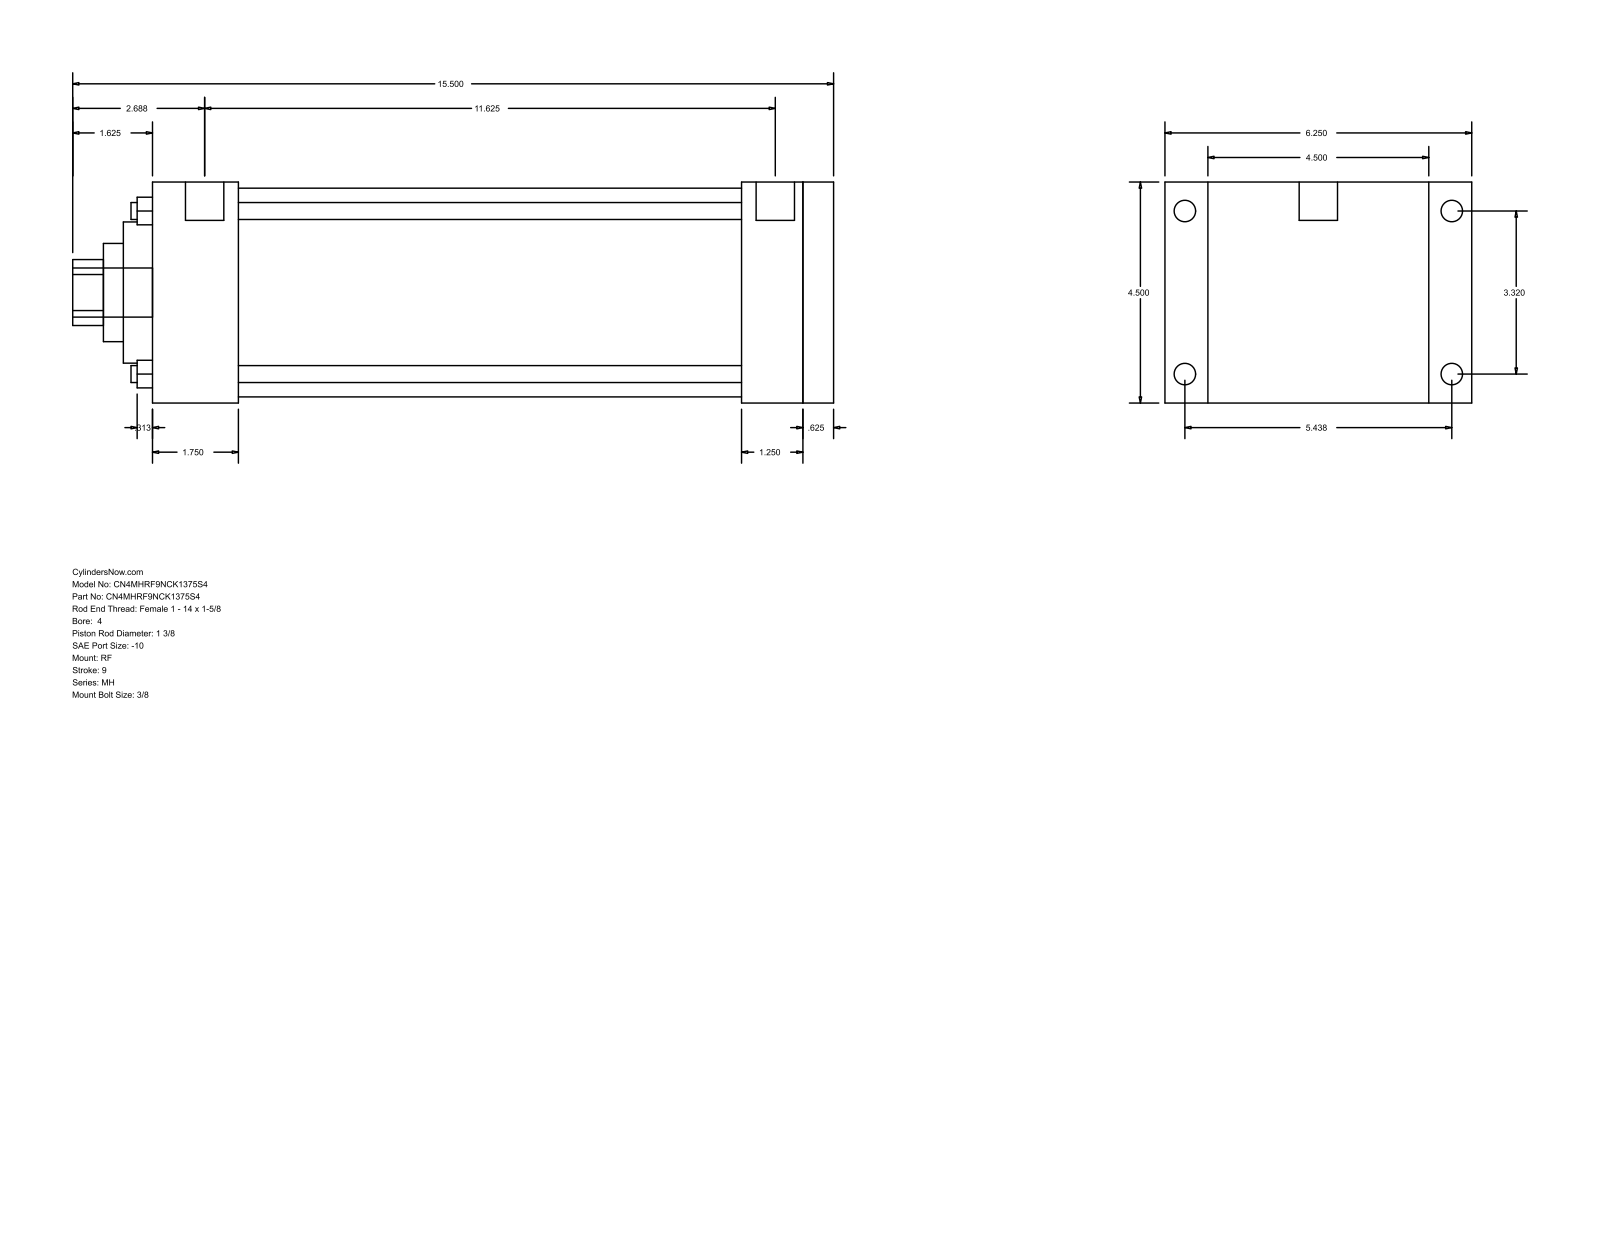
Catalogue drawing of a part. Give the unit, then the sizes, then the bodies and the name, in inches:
Units: inches
Overall size (bounding box): 15.5 × 6.25 × 4.5
Round holes (diameter × count): ⌀0.345 ×4, ⌀1.375 ×1, ⌀2 ×1, ⌀2.875 ×1, ⌀4.25 ×1
Round bosses / shafts (diameter × count): ⌀0.438 ×4, ⌀0.344 ×4, ⌀0.781 ×2, ⌀1 ×1
Partial cylindrical surfaces — rounded edges, fillets, slot ends (radius × count): R0.672 ×1
Main face-to-face distances: 4.5, 13.875, 0.625, 13.25, 1.75, 11.5, 12.125, 12, 10.25, 1.25
Hole centre spacings: 2.347, 3.32, 4.695
Bodies: 0 solids, 94 faces (65 planar, 29 cylindrical, 0 other)
Part name (STEP PRODUCT): MH_RF__0400_1.375
STEP written by: GSSL Pune (CONFIG_CONTROL_DESIGN)
